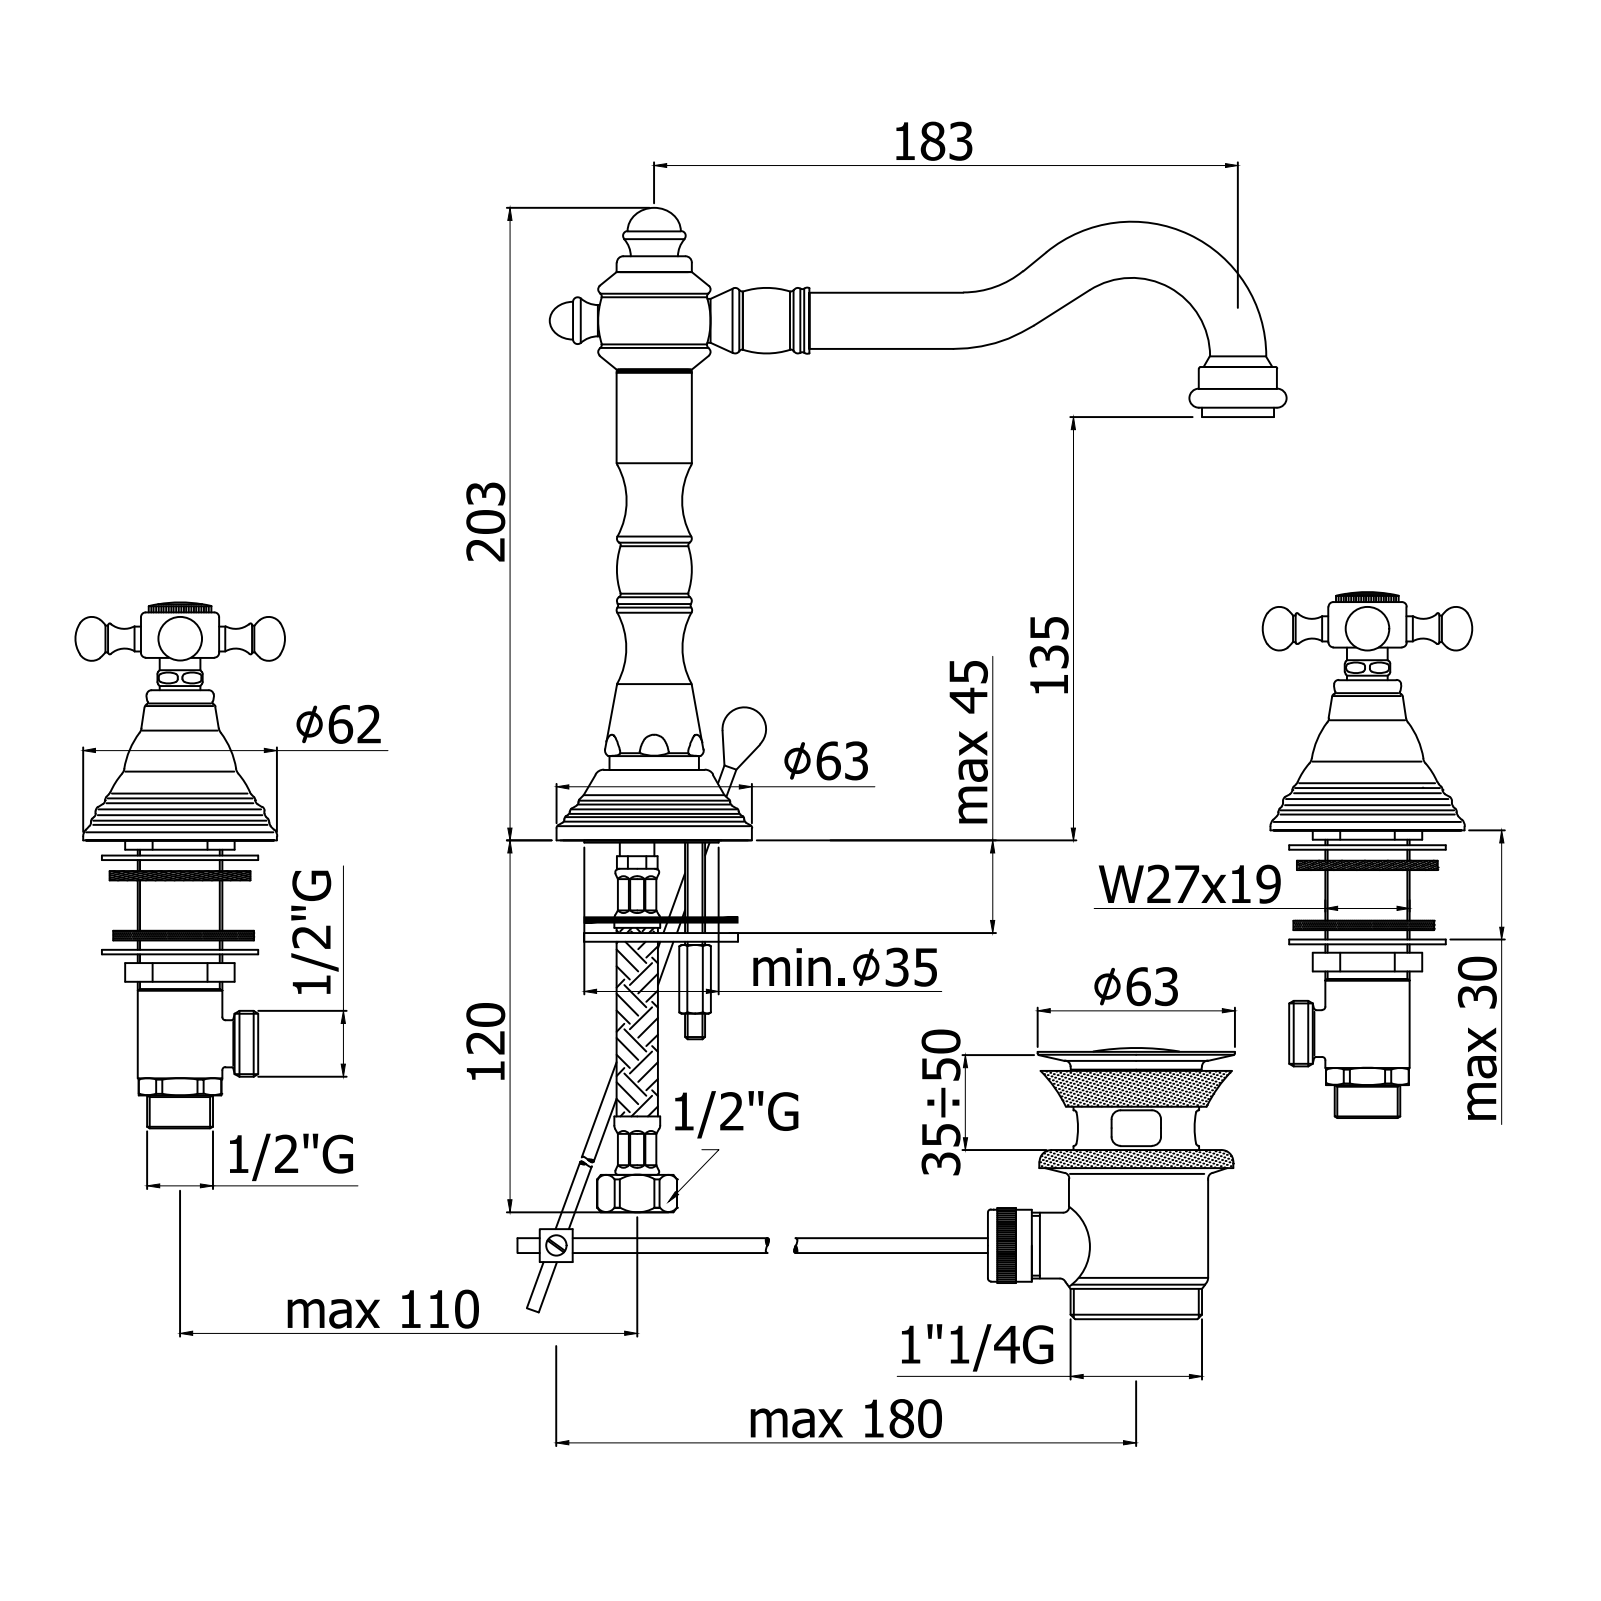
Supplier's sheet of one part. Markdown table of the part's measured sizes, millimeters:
| quantity | value |
| --- | --- |
| part name | FBLV055CR |
| STEP written by | CREO PARAMETRIC BY PTC INC, 2020044 (CONFIG_CONTROL_DESIGN) |
| units | millimeters |
| bodies | 3 solids, 1106 faces (460 planar, 322 cylindrical, 324 other) |
| overall size | 264.07 × 234.73 × 204.4 |
| volume | 353 654 mm³ |
| surface area | 77 064 mm² |
| round holes (diameter × count) | 5 × 2, 9 × 2, 10 × 2, 11 × 2, 5.5 × 1, 20 × 1, 24.1 × 1, 48.5 × 1 |
| round bosses / shafts (diameter × count) | 25 × 3, 9 × 3, 7 × 3, 63 × 2, 22.5 × 2, 18 × 2, 14 × 2, 13 × 2 |
| partial cylindrical surfaces (radius × count) | 11 × 2 |
| main face-to-face distances | 30, 60.4, 135.6, 75.2, 2, 58.4, 133.6, 28.4, 32, 103.6 |
| hole center spacings | 9.01, 13.46, 13.6, 22.61, 15, 22 |
